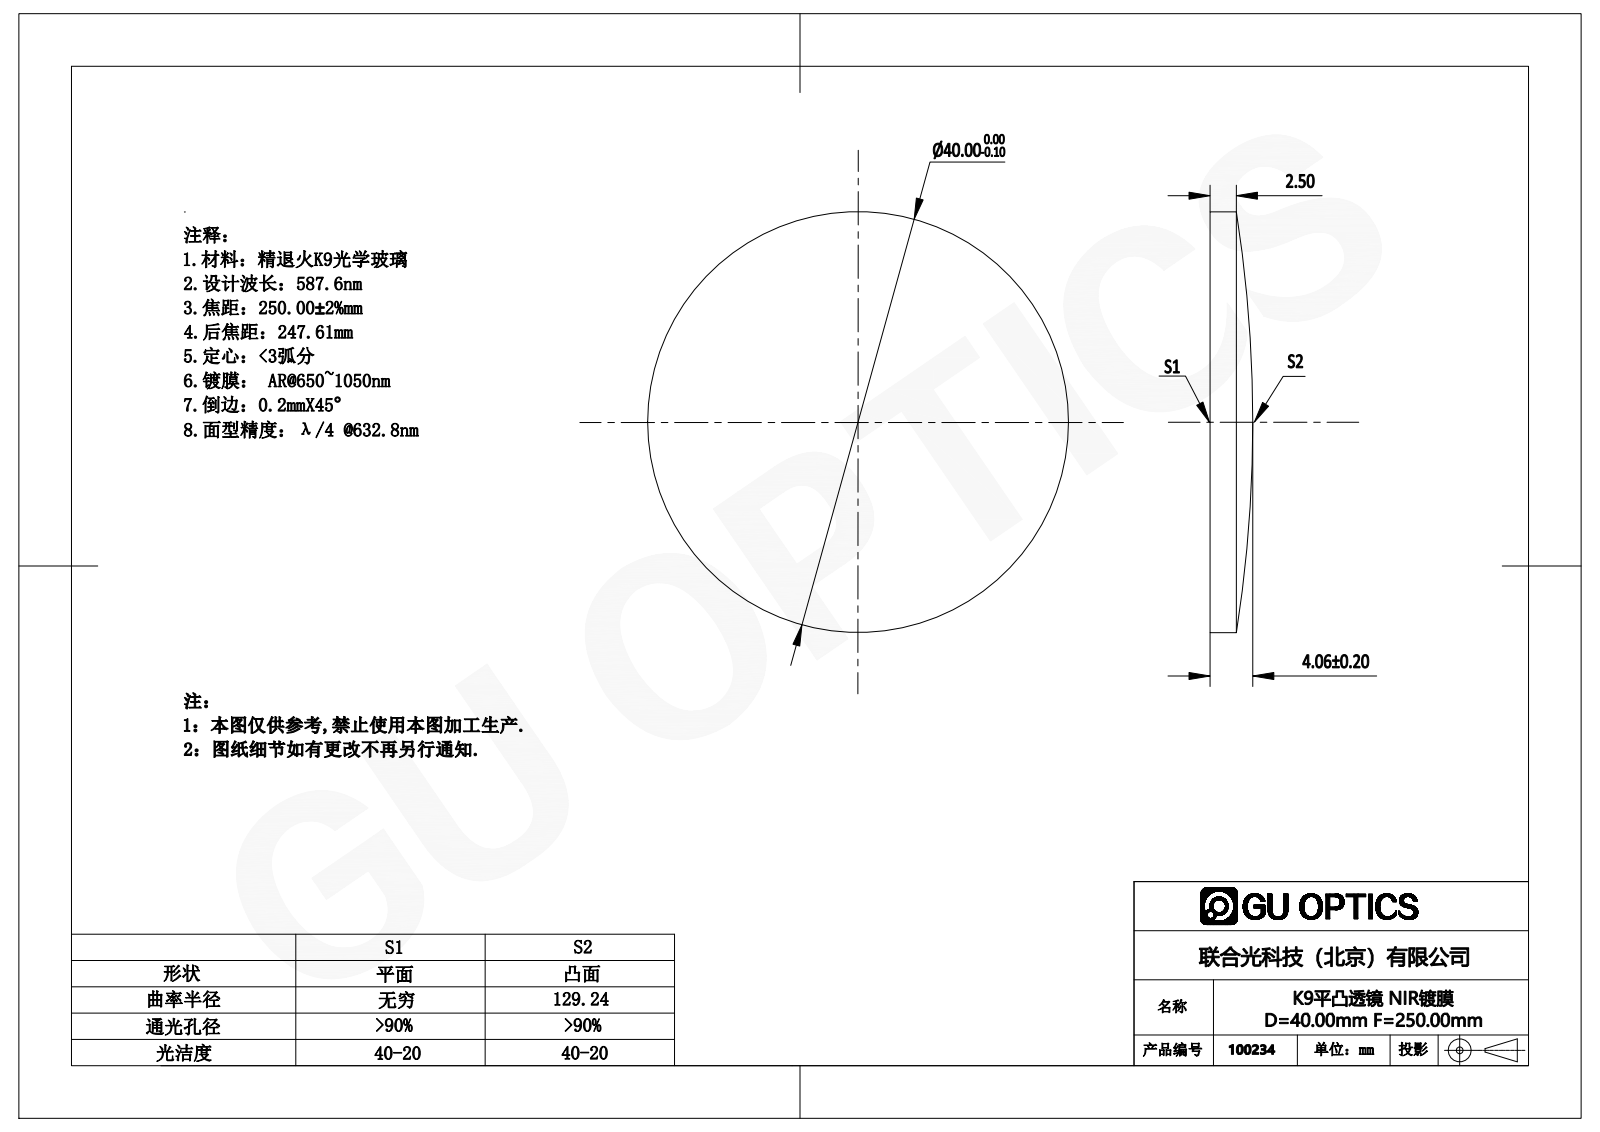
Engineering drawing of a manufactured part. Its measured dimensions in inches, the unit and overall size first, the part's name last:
Units: inches
Overall size (bounding box): 1.575 × 1.575 × 0.16
Round bosses / shafts (diameter × count): ⌀1.575 ×1
Volume: 0.252 in³ · Surface area: 4.394 in²
Bodies: 1 solid, 5 faces (1 planar, 2 cylindrical, 2 other)
Part name (STEP PRODUCT): 100234
STEP written by: SolidWorks 2016 (AUTOMOTIVE_DESIGN)
